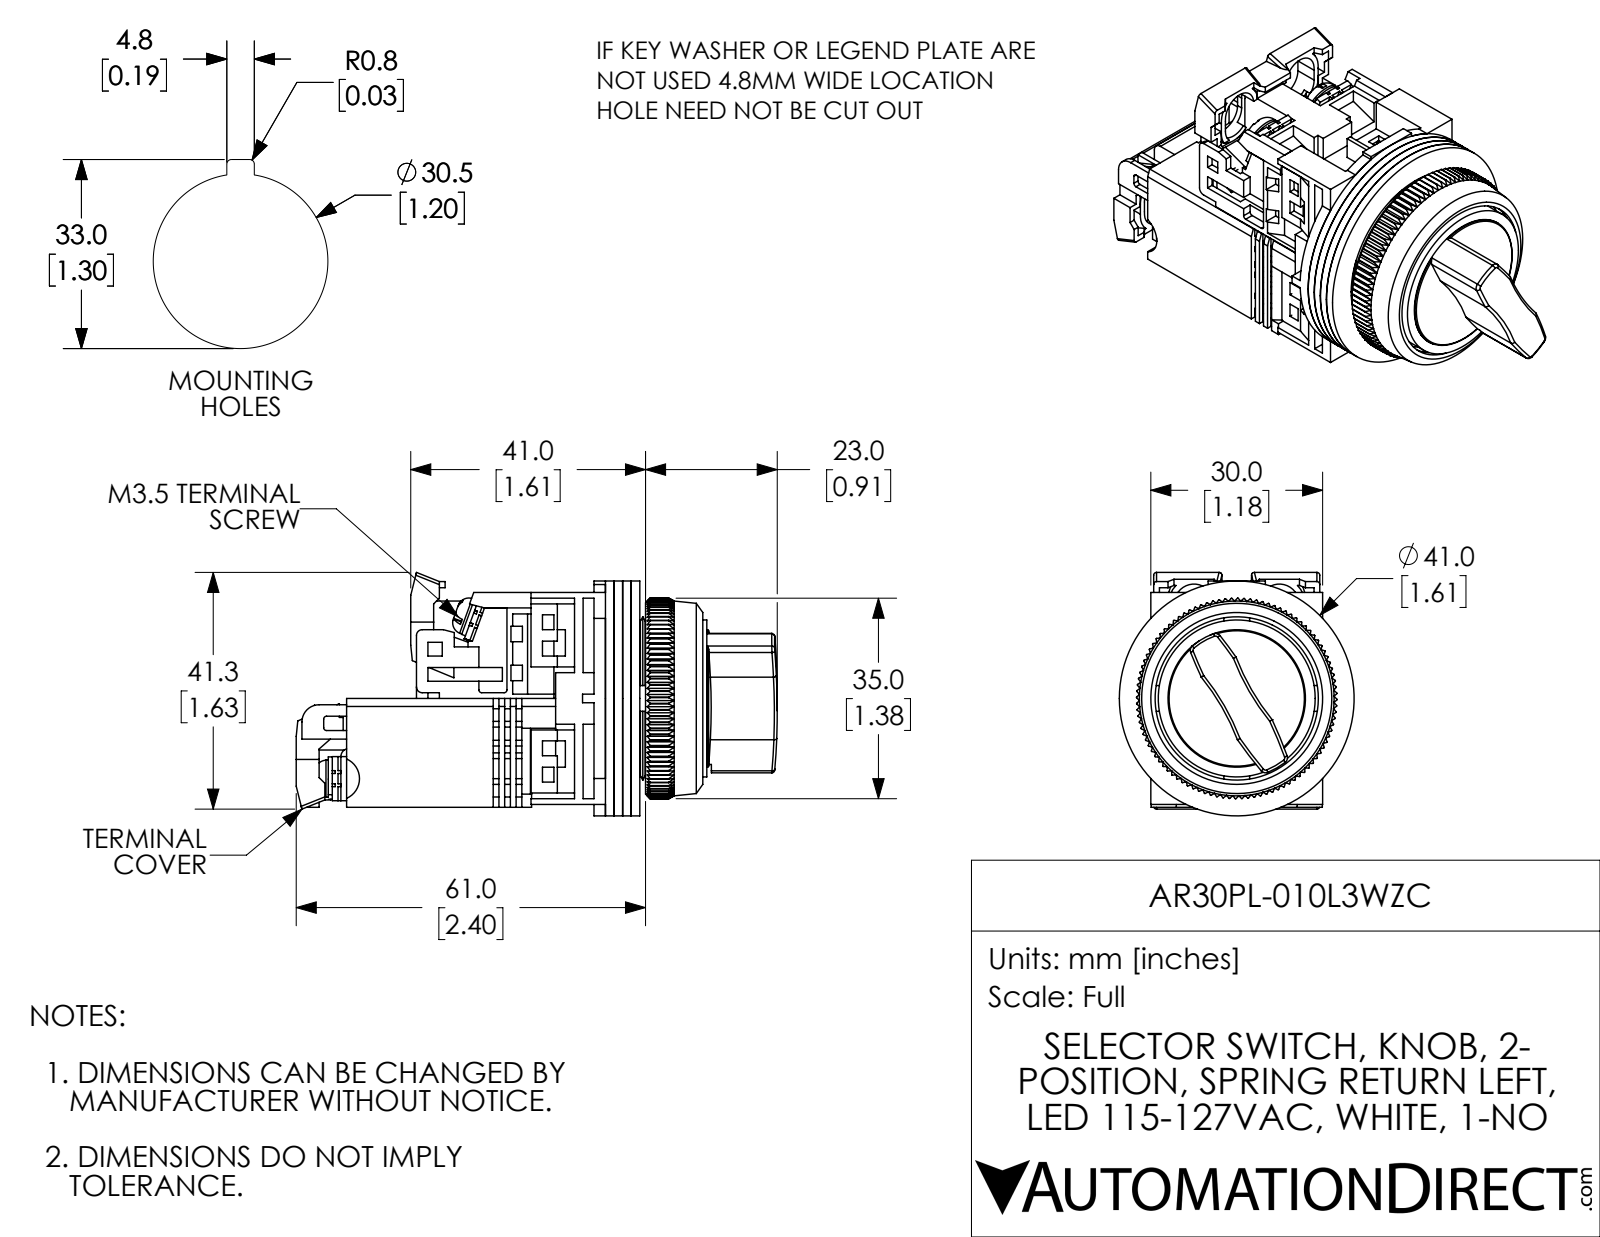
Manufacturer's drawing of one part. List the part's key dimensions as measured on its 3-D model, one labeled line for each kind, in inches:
Part name (STEP PRODUCT): AR30PL-010L3WZC
STEP written by: SolidWorks 2017 (AUTOMOTIVE_DESIGN)
Units: inches
Bodies: 27 solids, 2357 faces (1706 planar, 321 cylindrical, 330 other)
Overall size (bounding box): 3.307 × 1.673 × 1.614
Volume: 3.001 in³ · Surface area: 63.38 in²
Round holes (diameter × count): ⌀0.138 ×6, ⌀0.142 ×4, ⌀0.118 ×3, ⌀0.472 ×1, ⌀0.709 ×1, ⌀0.768 ×1, ⌀0.827 ×1, ⌀1.122 ×1, ⌀1.181 ×1, ⌀1.252 ×1
Round bosses / shafts (diameter × count): ⌀0.26 ×4, ⌀0.138 ×2, ⌀0.063 ×2, ⌀1.614 ×1, ⌀1.15 ×1, ⌀1.079 ×1, ⌀0.945 ×1, ⌀0.886 ×1
Partial cylindrical surfaces — rounded edges, fillets, slot ends (radius × count): R0.059 ×17, R0.02 ×13, R0.039 ×6, R0.138 ×4, R0.177 ×4, R0.118 ×2, R1.575 ×2, R2.953 ×2
Main face-to-face distances: 0.059, 0.118, 0.177, 0.079, 0.039, 0.748, 0.787, 0.197, 0.256, 1.417
Hole centre spacings: 0.579, 0.297, 0.624, 0.02, 0.302, 0.583, 0.583, 0.606
